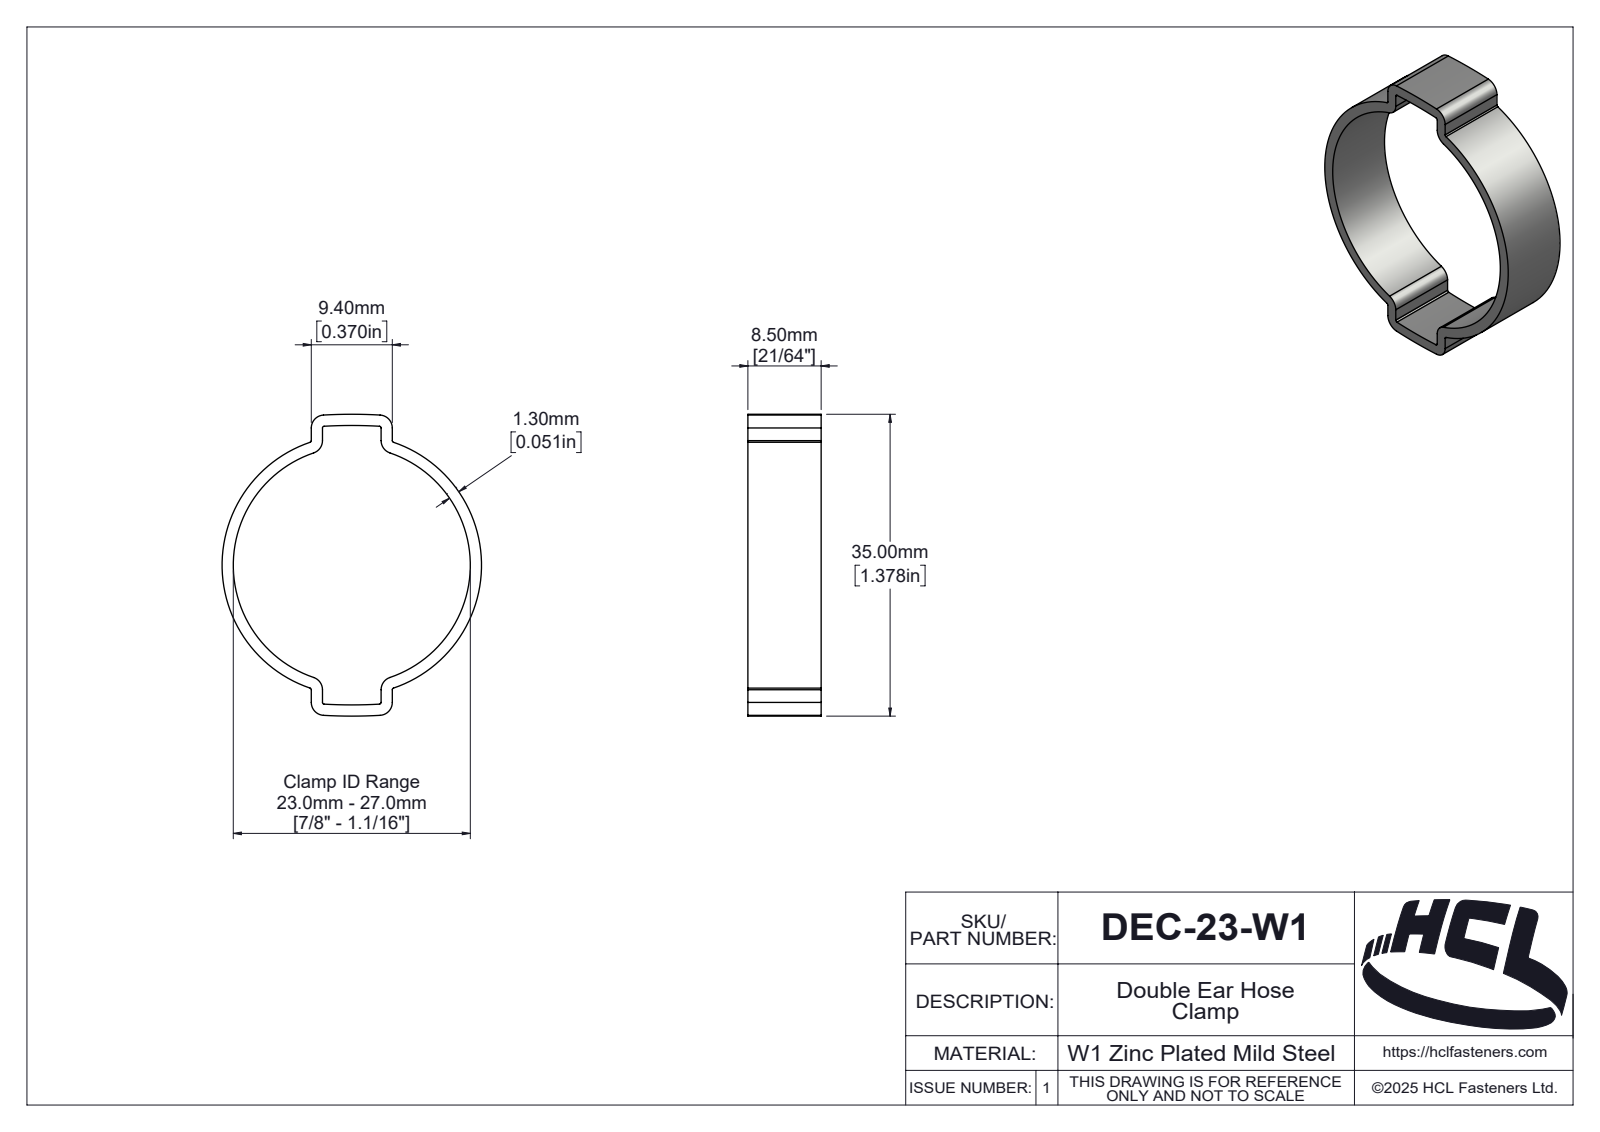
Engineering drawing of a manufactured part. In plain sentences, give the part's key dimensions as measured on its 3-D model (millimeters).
The part is named "DEC-23-W1". Its 3-D file was written by "SolidWorks 2025 (AUTOMOTIVE_DESIGN)". It is 1 solid with 137 faces: 12 planar, 67 cylindrical and 58 other. Overall it measures 35 by 30.1 by 8.5 millimeters. Its volume is 1 103 cubic millimeters and its surface area 1 962 square millimeters. Partial cylindrical surfaces (rounded edges, fillets, slot ends): 8 of radius 0.2, 8 of radius 1.5, 2 of radius 57.85, 2 of radius 59.15, 1 of radius 0.2, 1 of radius 0.81, 1 of radius 1.01, 1 of radius 1.06. The main face-to-face distances are 8.5, 1.3, 8.1, 9.4, 6.8, 4.58, 3.28, 3.52, 4.82, 4.43.
